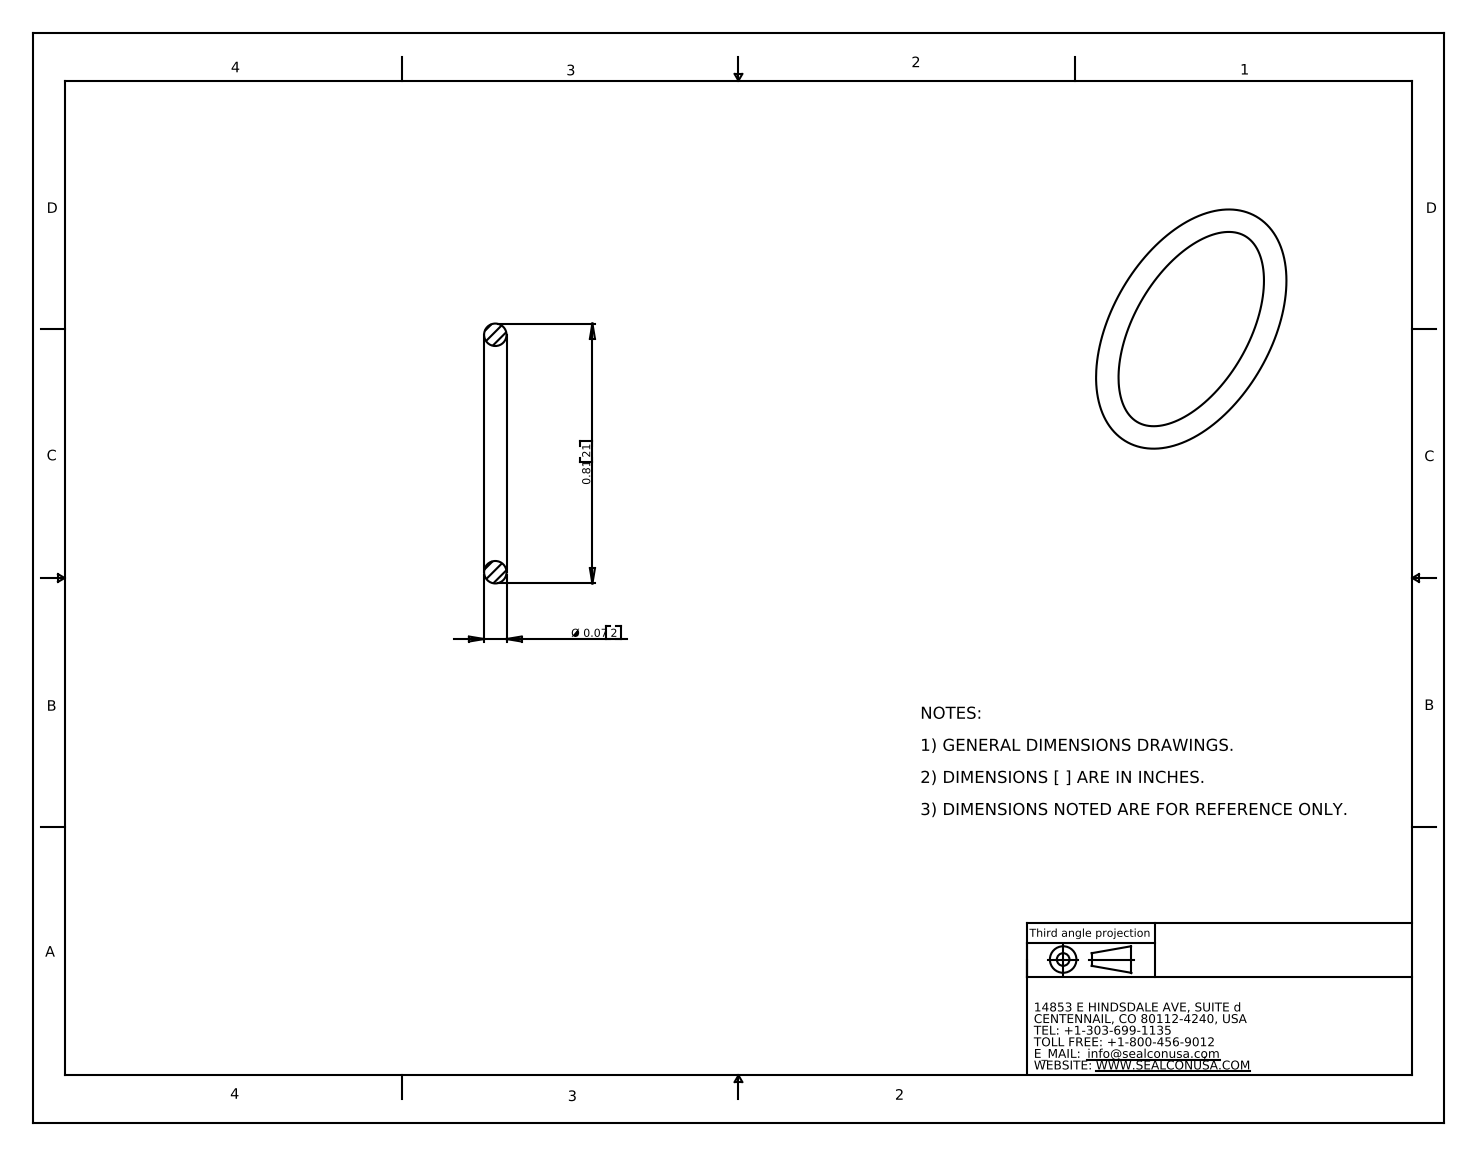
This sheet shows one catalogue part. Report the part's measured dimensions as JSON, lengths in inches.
{"part_name": "OM-20-VT", "step_written_by": "SolidWorks 2007 (CONFIG_CONTROL_DESIGN)", "units": "inches", "bodies": {"solids": 1, "faces": 4, "planar": 0, "cylindrical": 0, "other": 4}, "overall_size": [0.81, 0.81, 0.07], "volume_in3": 0.009, "surface_area_in2": 0.511}
